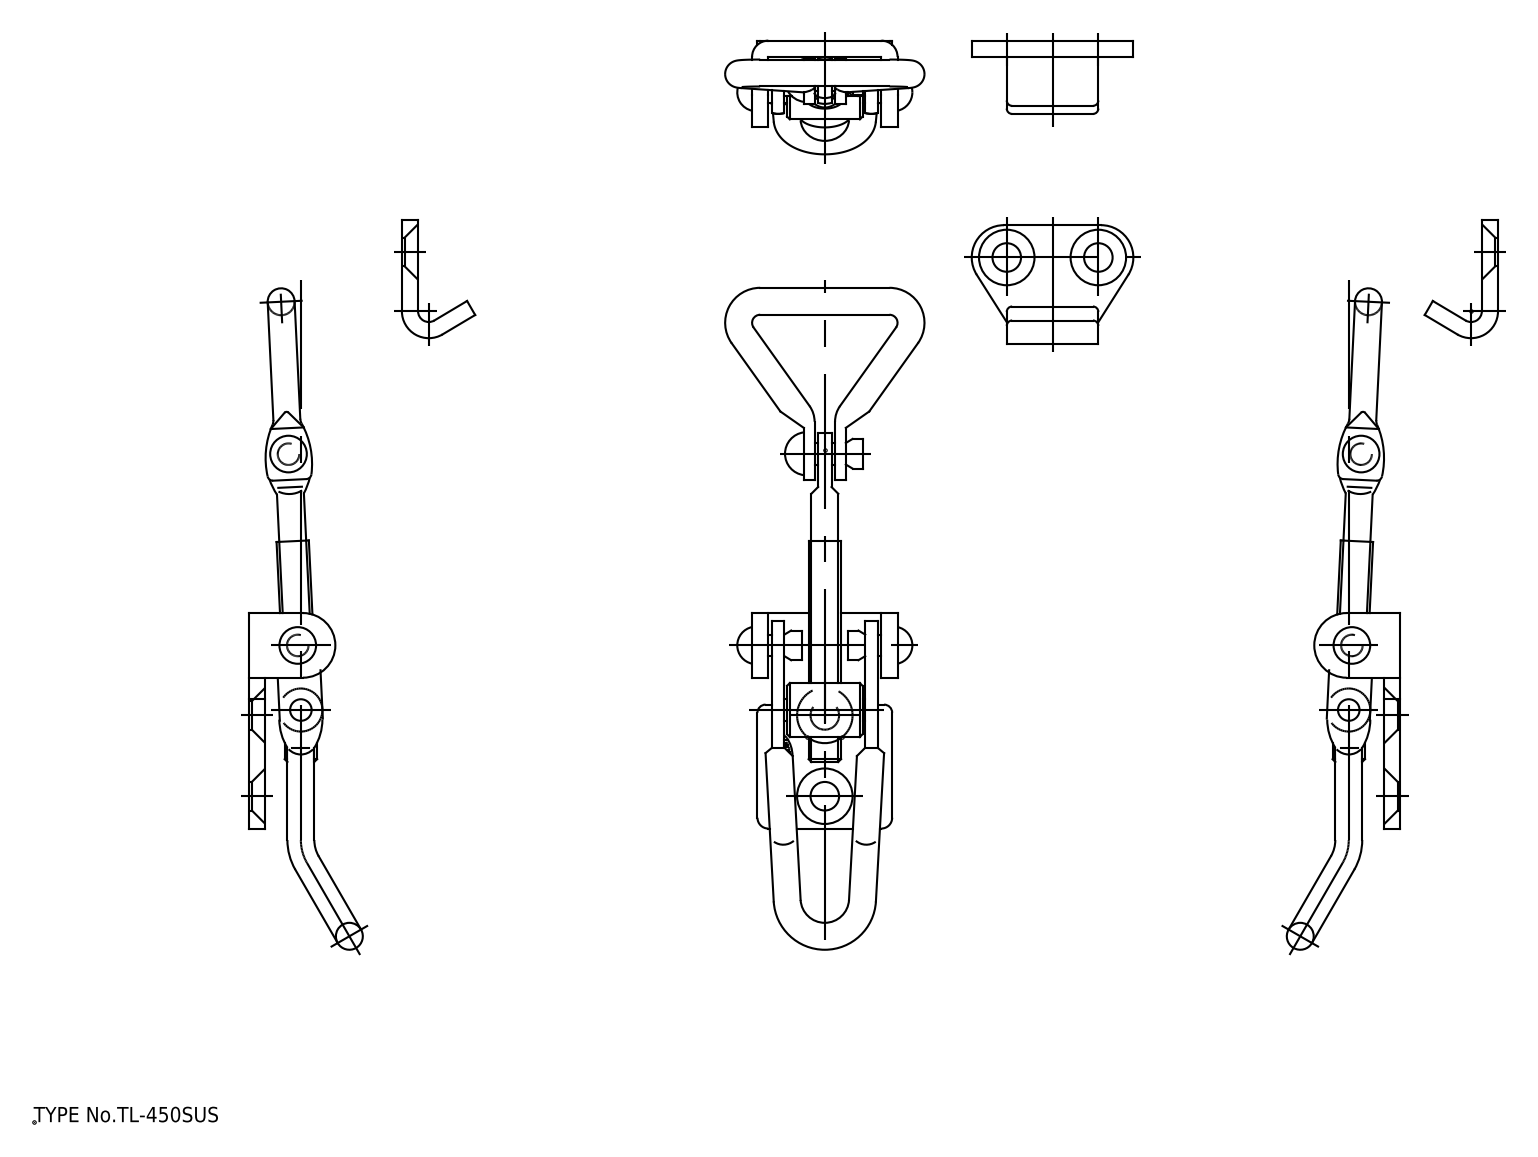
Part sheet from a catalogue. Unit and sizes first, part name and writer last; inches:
Units: inches
Overall size (bounding box): 5.317 × 1.457 × 0.831
Round holes (diameter × count): ⌀0.209 ×4, ⌀0.157 ×3, ⌀0.236 ×1
Round bosses / shafts (diameter × count): ⌀0.197 ×8, ⌀0.394 ×1, ⌀0.236 ×1, ⌀0.217 ×1
Partial cylindrical surfaces — rounded edges, fillets, slot ends (radius × count): R0.079 ×5, R0.039 ×4, R0.197 ×3, R0.236 ×3, R0.02 ×2, R0.035 ×2, R0.059 ×2, R0.118 ×2
Main face-to-face distances: 0.118, 0.039, 0.079, 0.827, 0.157, 0.091, 0.681, 0.028, 0.709, 0.799
Hole centre spacings: 3.384, 3.972, 0.472, 0.591, 0.669, 1.313, 1.785
Volume: 0.76 in³ · Surface area: 17.08 in²
Bodies: 6 solids, 222 faces (76 planar, 90 cylindrical, 56 other)
Part name (STEP PRODUCT): TL-450SUS-K; アーム; ソケット; ベース (+2 more)
STEP written by: spGate 19.8.4 (****-****-****-****) (AUTOMOTIVE_DESIGN)
